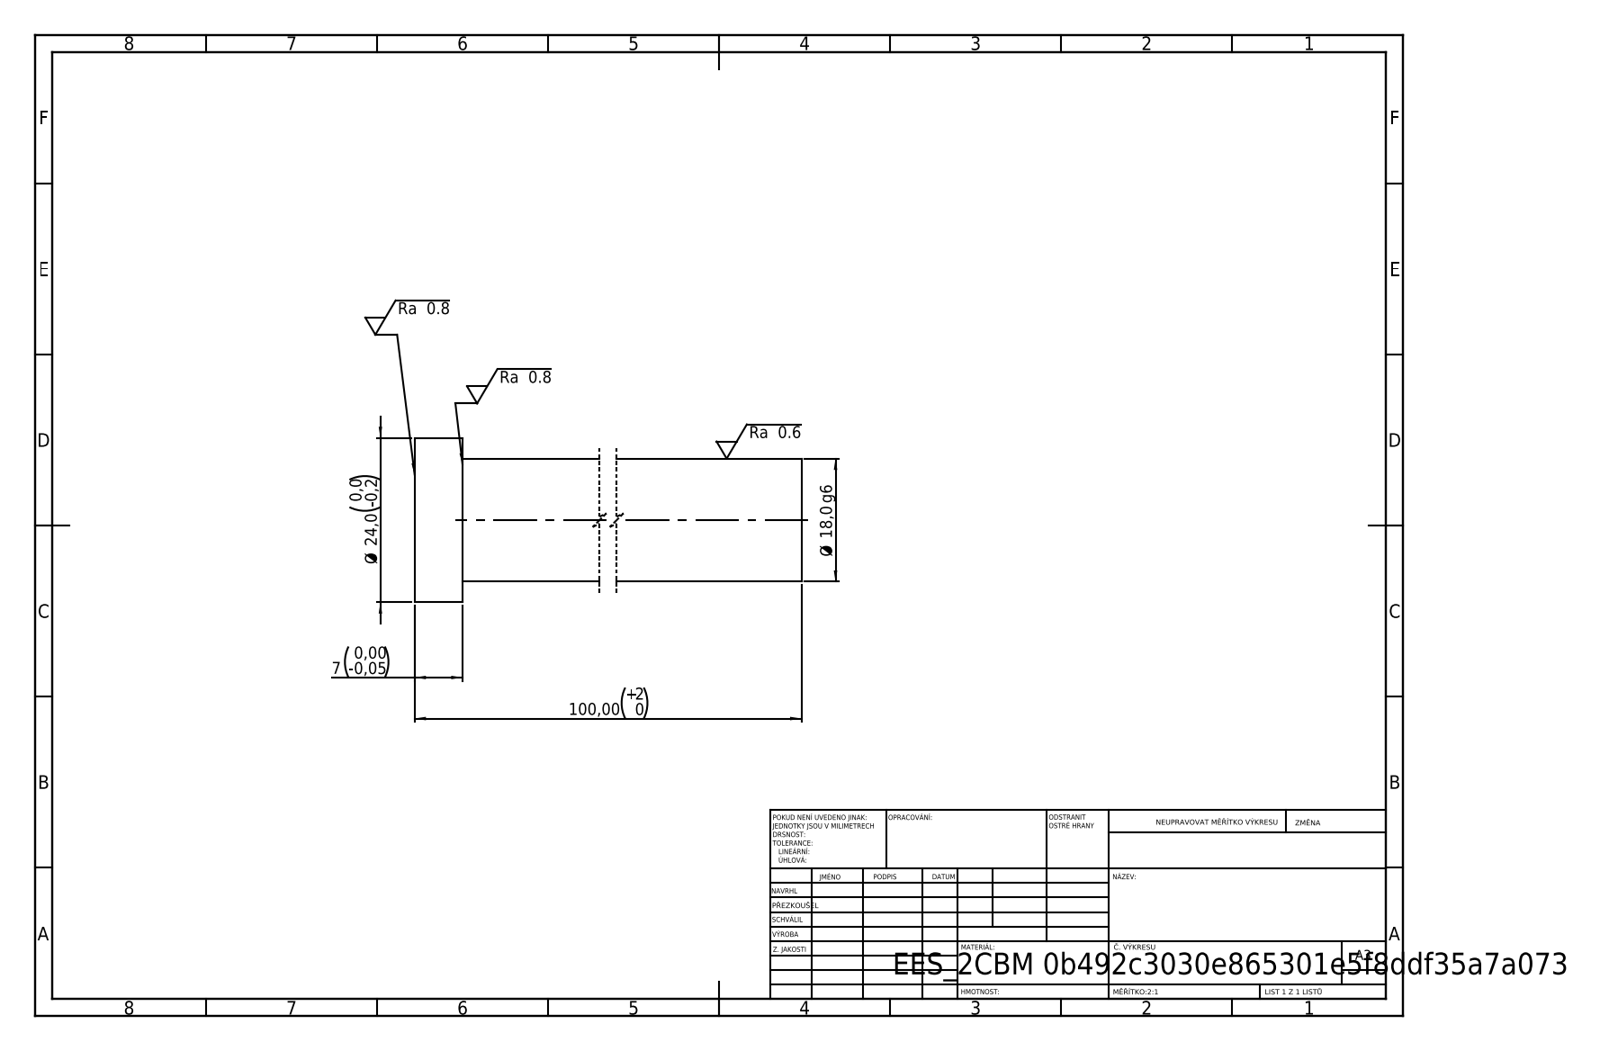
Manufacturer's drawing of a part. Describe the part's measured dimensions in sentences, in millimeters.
Its 3-D file was written by "SolidWorks 2019 (CONFIG_CONTROL_DESIGN)". It is 1 solid with 7 faces: 3 planar, 4 cylindrical and 0 other. Overall it measures 100 by 24 by 24 millimeters. Its volume is 26 832 cubic millimeters and its surface area 6 692 square millimeters. Round bosses or shafts: 1 of diameter 24, 1 of diameter 18. The main face-to-face distances are 100, 7, 93.
